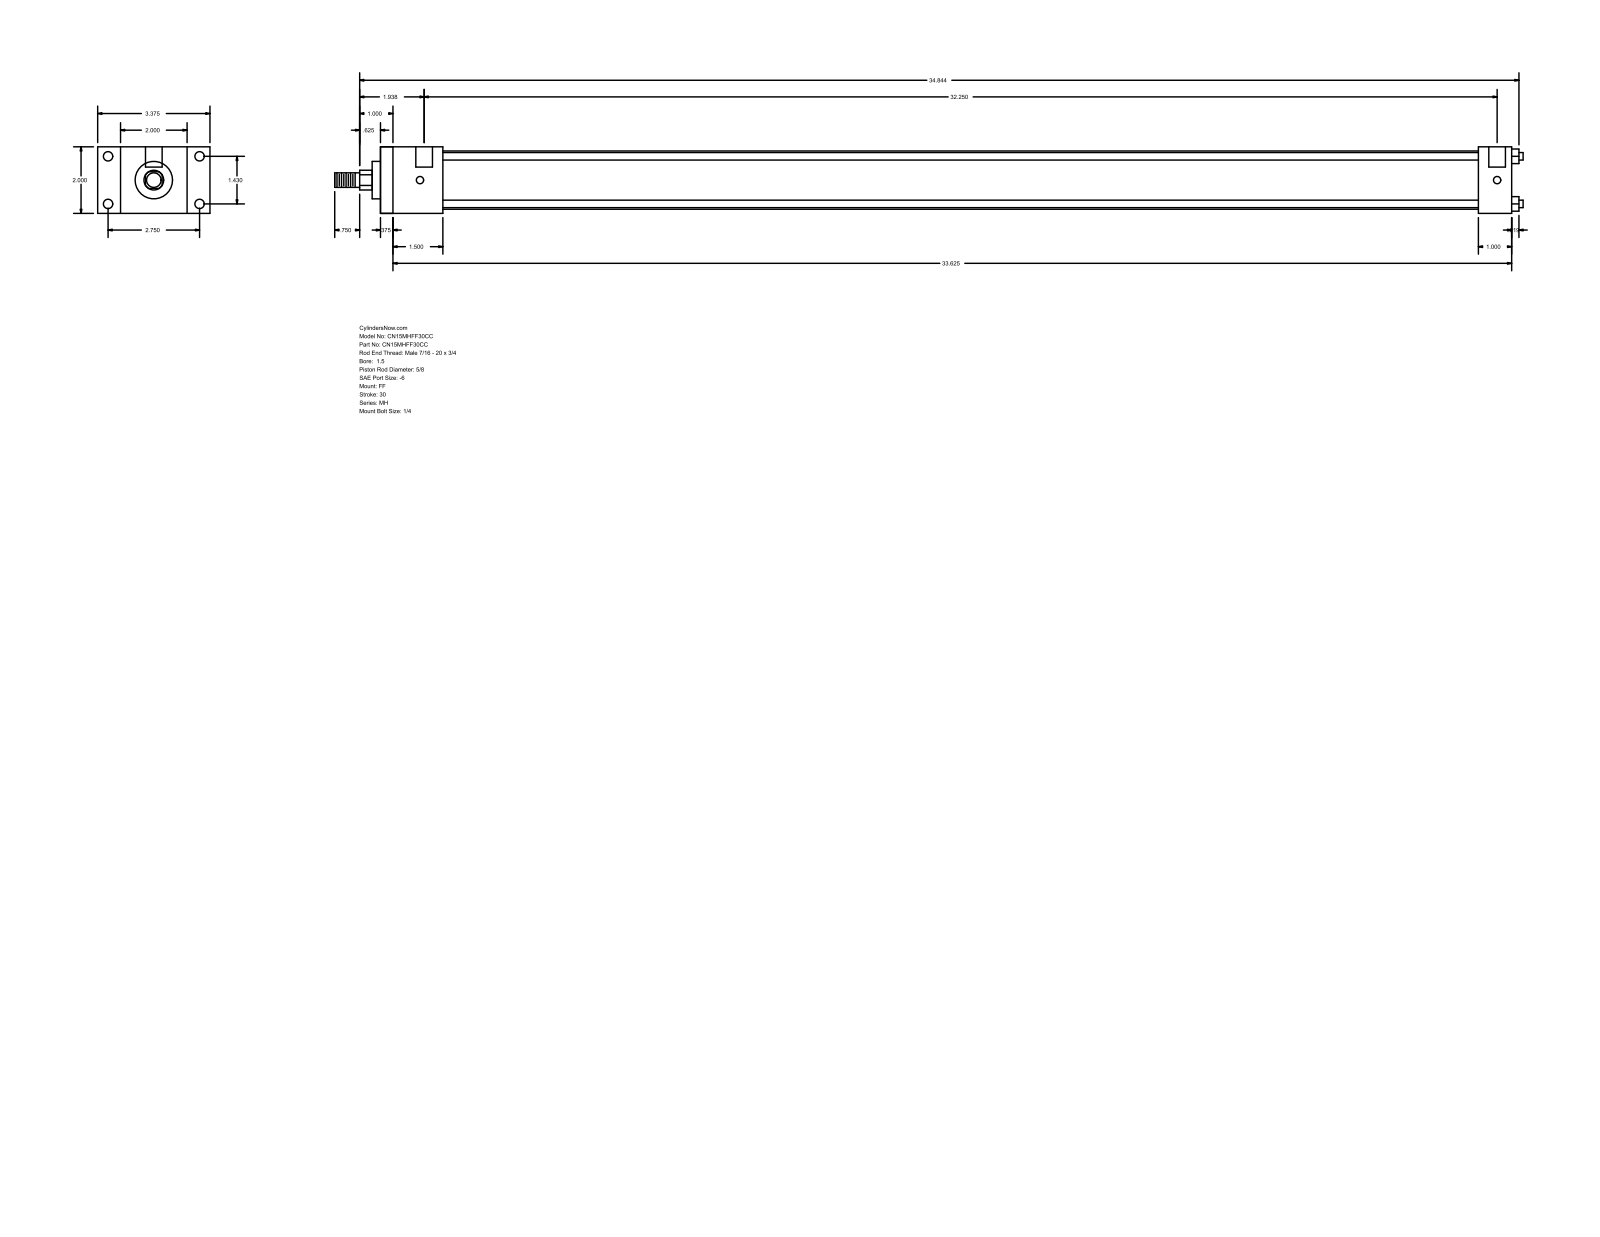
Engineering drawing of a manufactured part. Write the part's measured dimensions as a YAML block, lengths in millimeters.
part_name: "MH_FF__0150_0.625"
step_written_by: "GSSL Pune (CONFIG_CONTROL_DESIGN)"
units: millimeters
bodies: {solids: 0, faces: 92, planar: 64, cylindrical: 28, other: 0}
overall_size: [907.26, 85.72, 50.8]
round_holes:
  - {diameter: 5.56, count: 4}
  - {diameter: 7.14, count: 4}
  - {diameter: 12.7, count: 2}
round_bosses_or_shafts:
  - {diameter: 5.71, count: 4}
  - {diameter: 44.45, count: 1}
  - {diameter: 28.57, count: 1}
  - {diameter: 15.88, count: 1}
  - {diameter: 11.11, count: 1}
partial_cylinders:
  - {radius: 7.54, count: 1}
face_to_face_distances: [50.8, 863.6, 854.08, 9.52, 25.4, 17.46, 68.26, 47.62, 38.1, 815.98]
hole_center_spacings: [36.32, 69.84, 78.72, 822.32, 3.17, 819.15]
